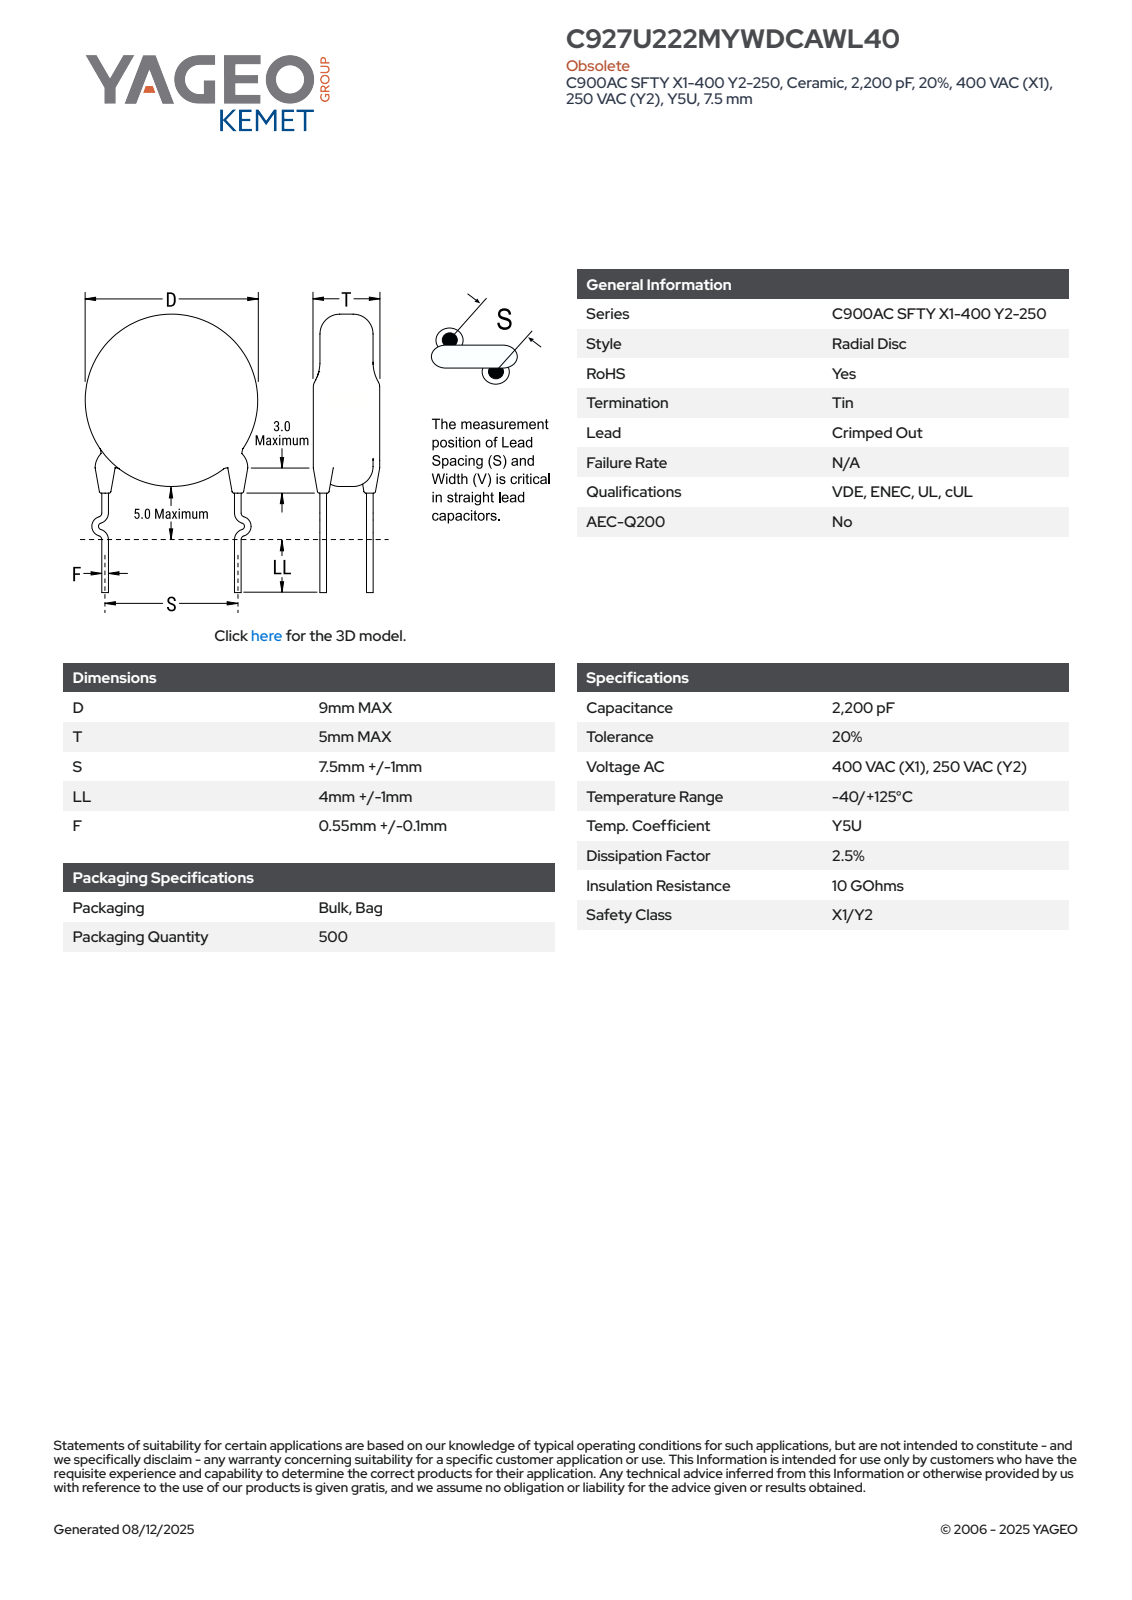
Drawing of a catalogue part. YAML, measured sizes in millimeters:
part_name: "CCD_KCOC900_D9T5S7.5LL5F0.55"
step_written_by: "SolidWorks 2014 (AUTOMOTIVE_DESIGN)"
units: millimeters
bodies: {solids: 4, faces: 87, planar: 63, cylindrical: 6, other: 18}
overall_size: [19, 12.29, 5]
volume: 319
surface_area: 312
round_bosses_or_shafts:
  - {diameter: 1.2, count: 2}
  - {diameter: 9, count: 1}
face_to_face_distances: [5, 0.94, 4.98, 4.04, 0.76, 3.82, 0.58, 4.07, 2.77, 2.88]
